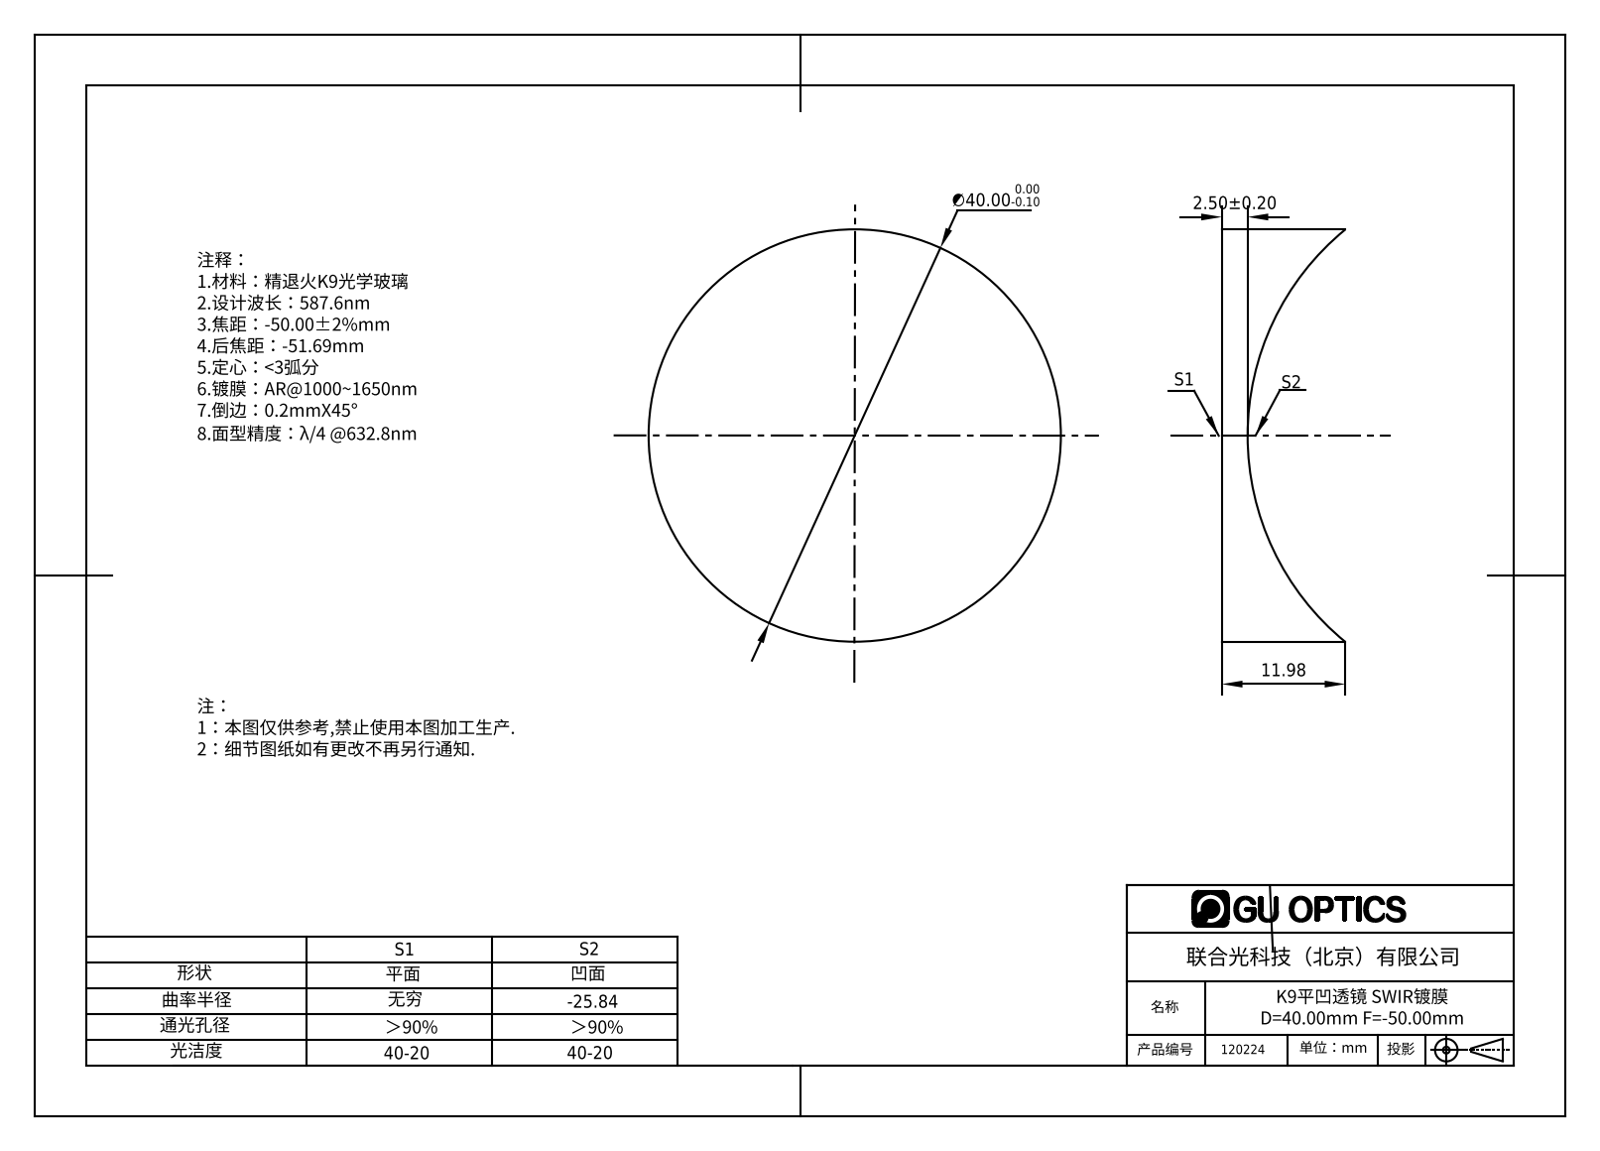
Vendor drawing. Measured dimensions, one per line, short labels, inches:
name: 120164
written by: SolidWorks 2016 (AUTOMOTIVE_DESIGN)
unit: in
bodies: 1 solid, 5 faces (1 planar, 2 cylindrical, 2 other)
size: 1.575 × 1.575 × 0.472
volume: 0.528 in³; area: 6.667 in²
bosses: 1× ⌀1.575
